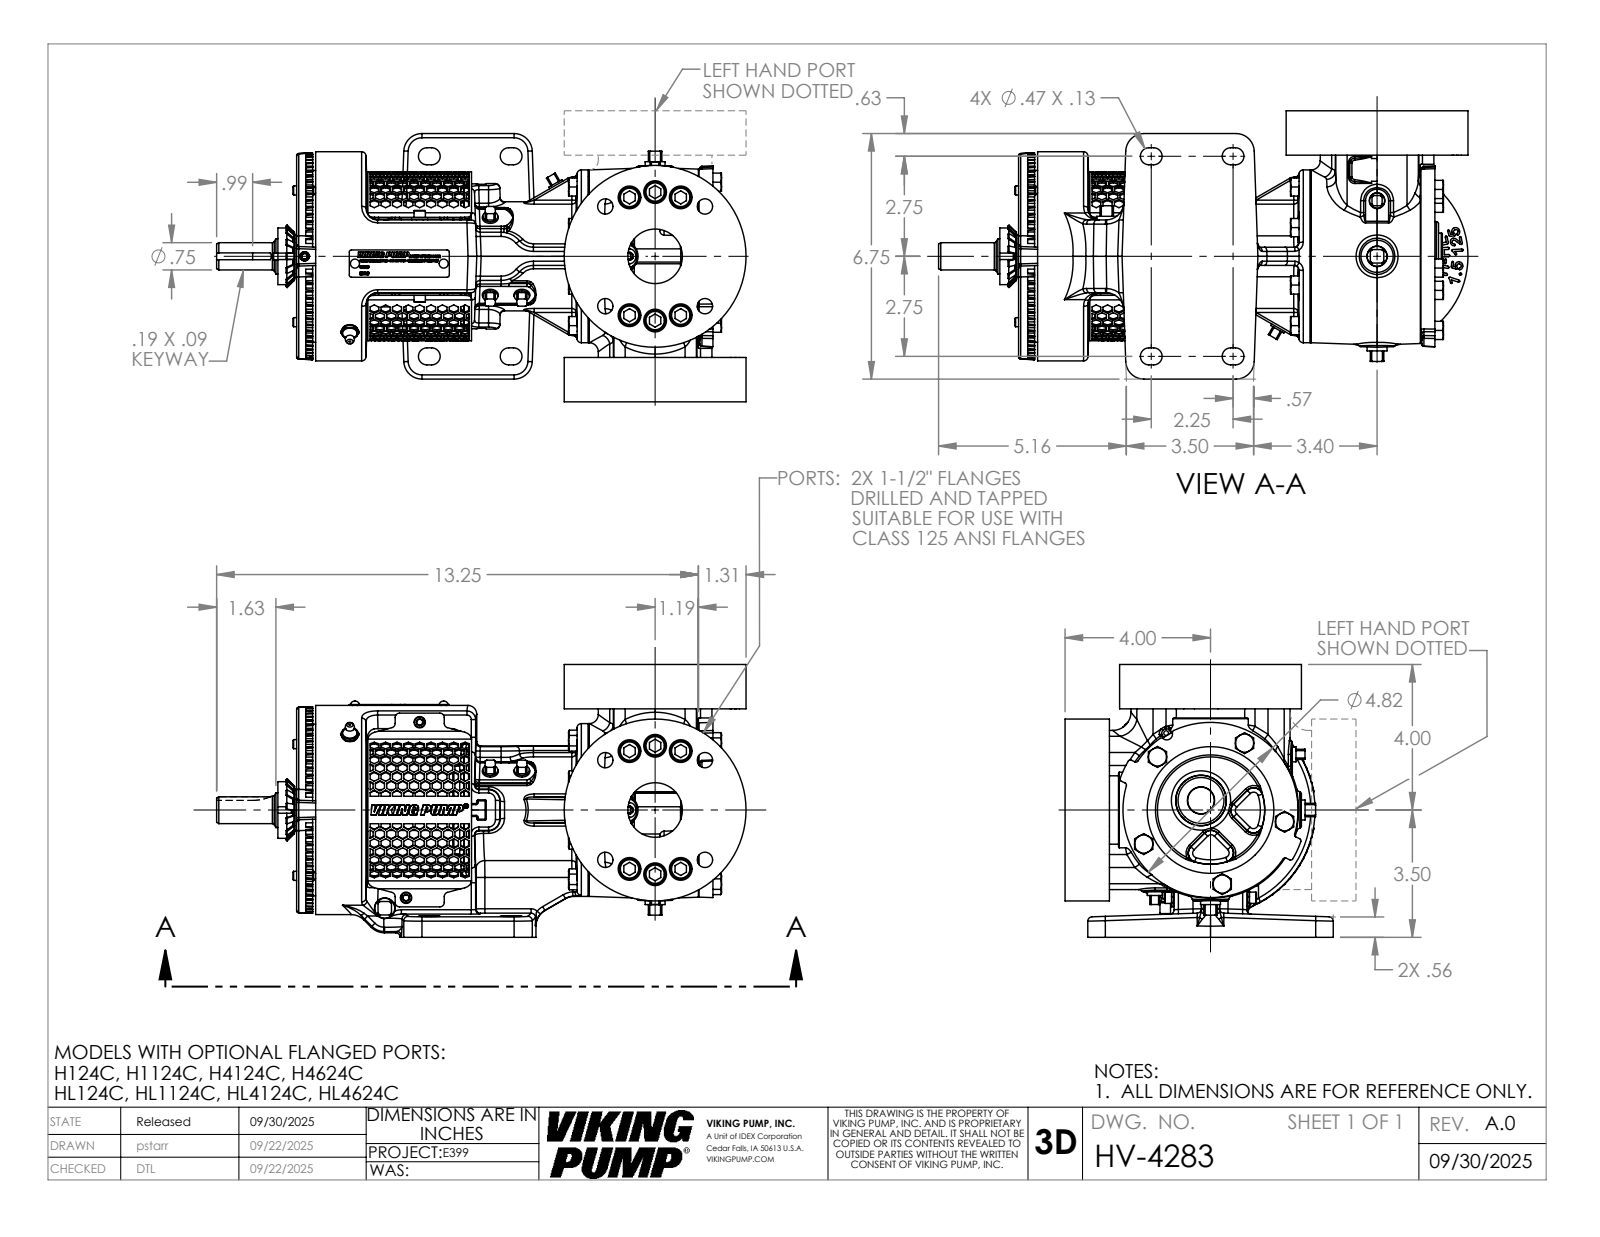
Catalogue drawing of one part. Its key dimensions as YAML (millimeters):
part_name: "HV-4283"
step_written_by: "SolidWorks 2024 (AUTOMOTIVE_DESIGN)"
units: millimeters
bodies: {solids: 1, faces: 4223, planar: 1441, cylindrical: 880, other: 1902}
overall_size: [369.79, 190.5, 187.32]
volume: 3648000
surface_area: 392647
round_holes:
  - {diameter: 6.35, count: 9}
  - {diameter: 15.88, count: 9}
  - {diameter: 10.72, count: 8}
  - {diameter: 4.04, count: 3}
  - {diameter: 5.02, count: 3}
  - {diameter: 15.87, count: 3}
  - {diameter: 6.53, count: 2}
  - {diameter: 38.1, count: 2}
  - {diameter: 25.03, count: 1}
  - {diameter: 25.12, count: 1}
  - {diameter: 32.13, count: 1}
  - {diameter: 114.35, count: 1}
round_bosses_or_shafts:
  - {diameter: 14.29, count: 12}
  - {diameter: 7.92, count: 3}
  - {diameter: 4.83, count: 3}
  - {diameter: 127, count: 2}
  - {diameter: 6.35, count: 2}
  - {diameter: 146.05, count: 1}
  - {diameter: 120.65, count: 1}
  - {diameter: 120.57, count: 1}
partial_cylinders:
  - {radius: 1.37, count: 140}
  - {radius: 3.05, count: 103}
  - {radius: 1.52, count: 49}
  - {radius: 12.7, count: 34}
  - {radius: 0.76, count: 22}
  - {radius: 6.1, count: 11}
  - {radius: 6.35, count: 10}
  - {radius: 5.95, count: 8}
face_to_face_distances: [30.99, 190.5, 49.28, 159.51, 290.8, 241.52, 13.3, 35.98, 277.5, 11.18]
hole_center_spacings: [44.85, 65.03, 18.07, 18.26, 36.22, 49.21, 53.06, 69.6]
